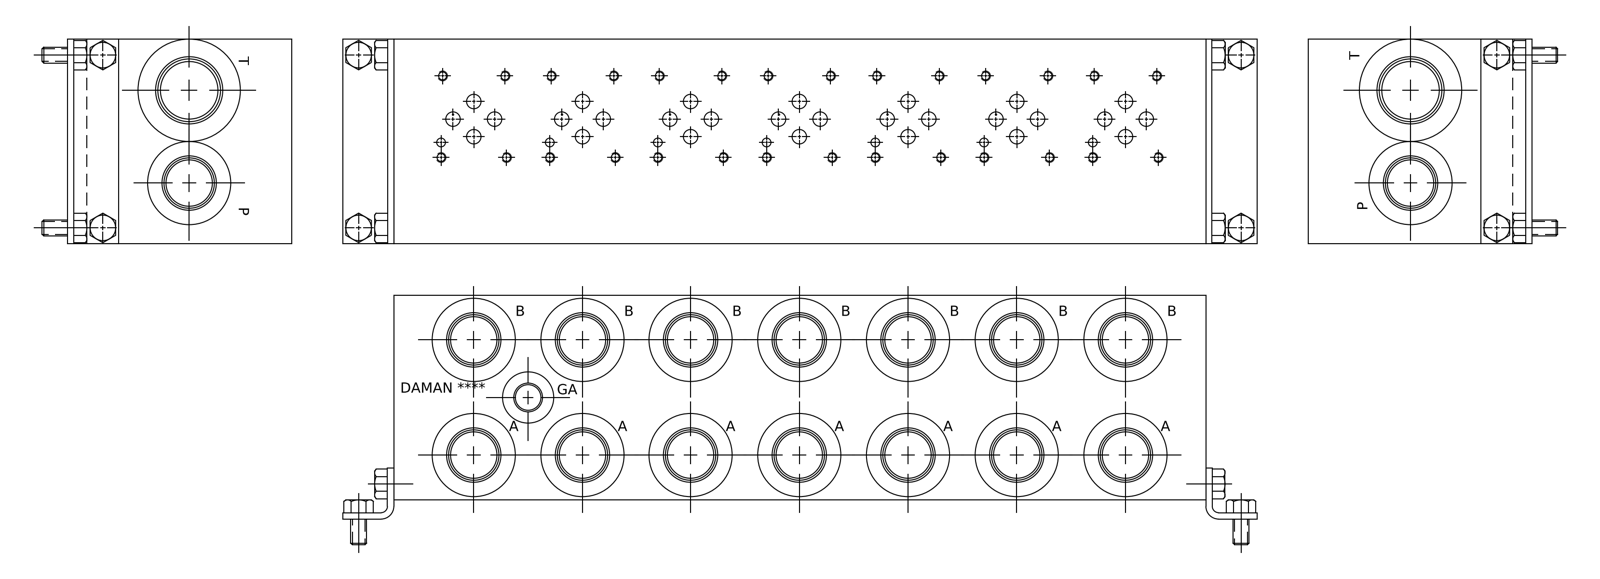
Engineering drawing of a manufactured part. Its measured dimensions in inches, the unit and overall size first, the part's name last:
Units: inches
Overall size (bounding box): 15.875 × 4 × 4
Round holes (diameter × count): ⌀0.149 ×28, ⌀0.19 ×28, ⌀0.25 ×21, ⌀0.906 ×15, ⌀0.981 ×15, ⌀1.08 ×15, ⌀1.655 ×15, ⌀1.063 ×14, ⌀0.156 ×7, ⌀0.281 ×7, ⌀0.422 ×7, ⌀0.257 ×2
Main face-to-face distances: 4, 0.031, 3.969, 15.875, 15.844, 15.813, 0.781, 0.75, 3.219, 15.094
Hole centre spacings: 4.25, 2.125, 2.125, 8.5, 0.532, 0.533, 3.095, 6.375
Volume: 232 in³ · Surface area: 379.7 in²
Bodies: 1 solid, 1111 faces (535 planar, 202 cylindrical, 374 other)
Part name (STEP PRODUCT): Part_AD03HP072S_3D
STEP written by: Autodesk Inventor 2019 (AUTOMOTIVE_DESIGN)
